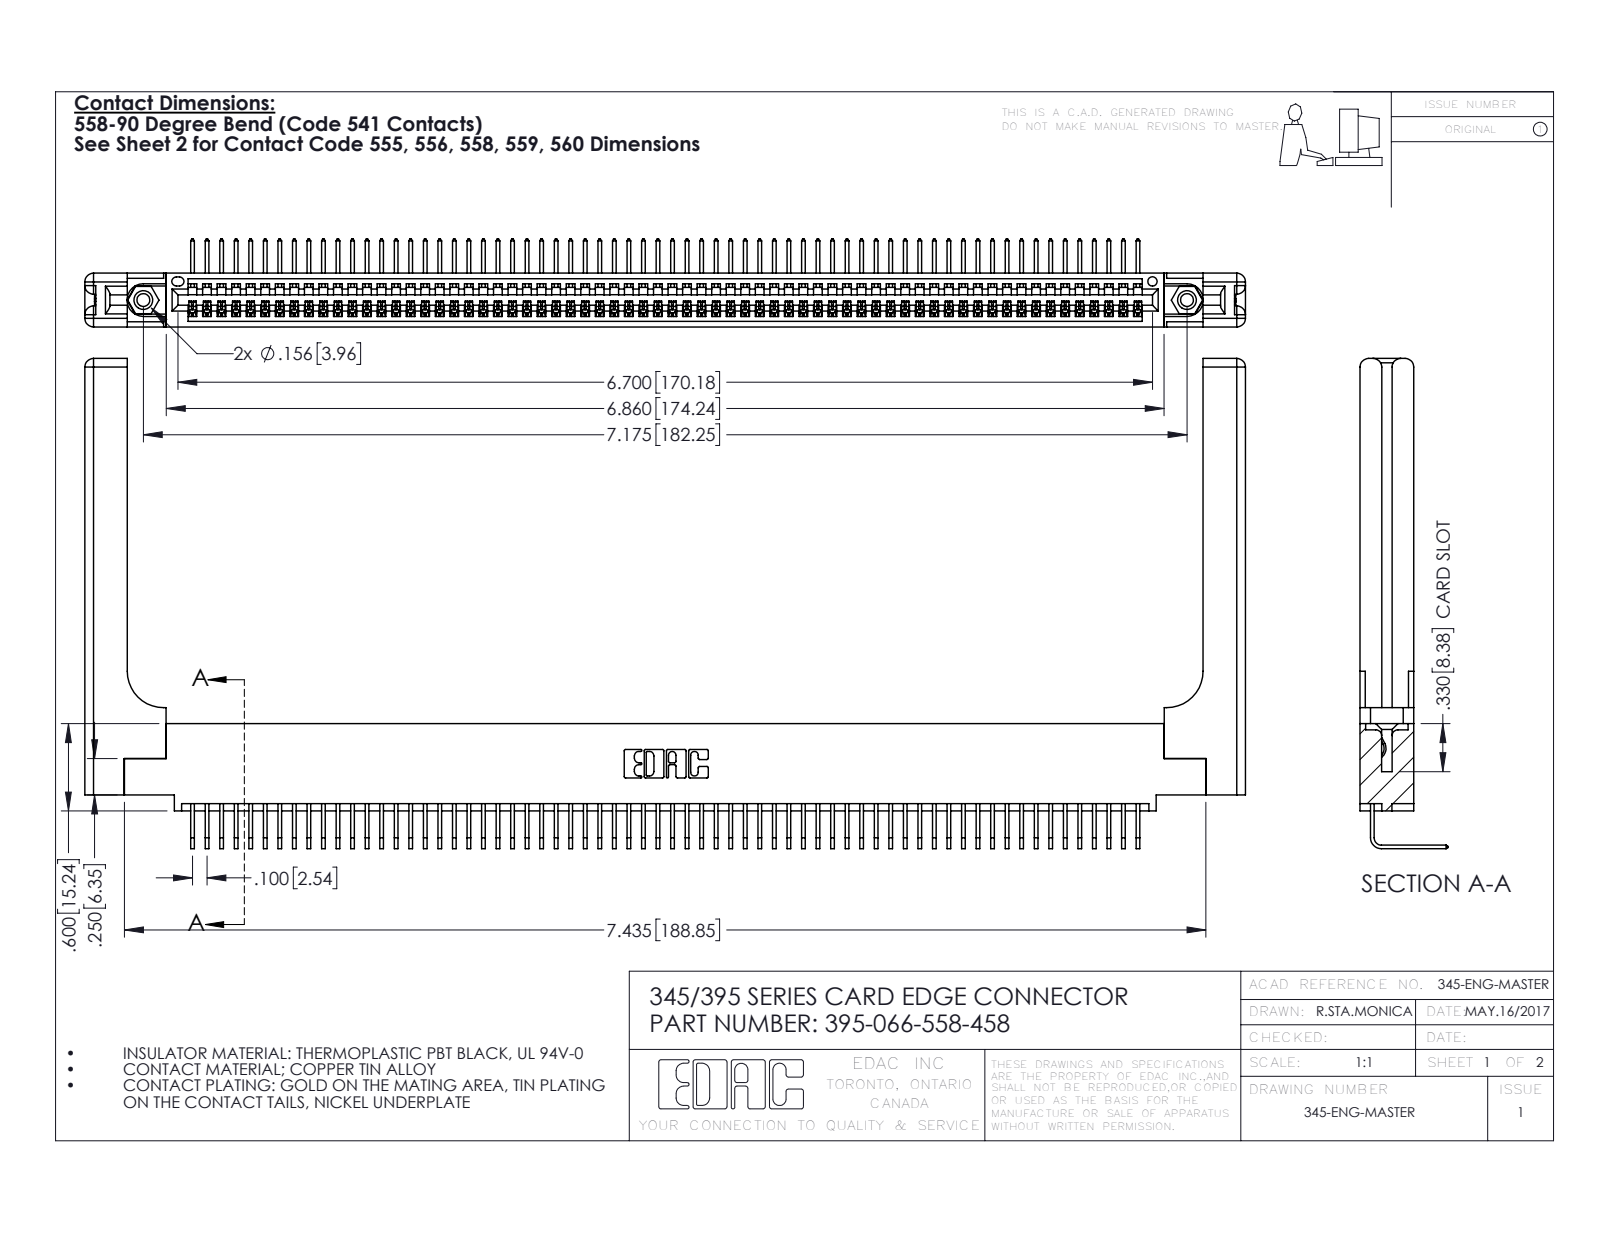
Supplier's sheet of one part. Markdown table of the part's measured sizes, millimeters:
| quantity | value |
| --- | --- |
| part name | 395-066-558-458; 345-220-058_345-220-058; 345-250-001_345-250-001-102; 345 Part_0.110 Offset - 0.156 Dia-TH (+1 more) |
| STEP written by | SolidWorks 2016 (CONFIG_CONTROL_DESIGN) |
| units | millimeters |
| bodies | 71 solids, 4346 faces (3004 planar, 1282 cylindrical, 60 other) |
| overall size | 202.7 × 85.6 × 15.4 |
| volume | 28 100 mm³ |
| surface area | 33 050 mm² |
| round holes (diameter × count) | 2.3 × 2, 3.2 × 2, 4 × 2, 1.6 × 1 |
| round bosses / shafts (diameter × count) | 3.9 × 2 |
| partial cylindrical surfaces (radius × count) | 0.2 × 132, 0.3 × 22, 1.5 × 16, 0.2 × 6, 0.8 × 6, 0.7 × 3, 0.8 × 2, 0.8 × 2 |
| main face-to-face distances | 1.8, 7.6, 9.4, 2.5, 6.9, 0.6, 5.1, 5.7, 3.8, 3.8 |
| hole center spacings | 6.9, 176.3, 182.2 |
